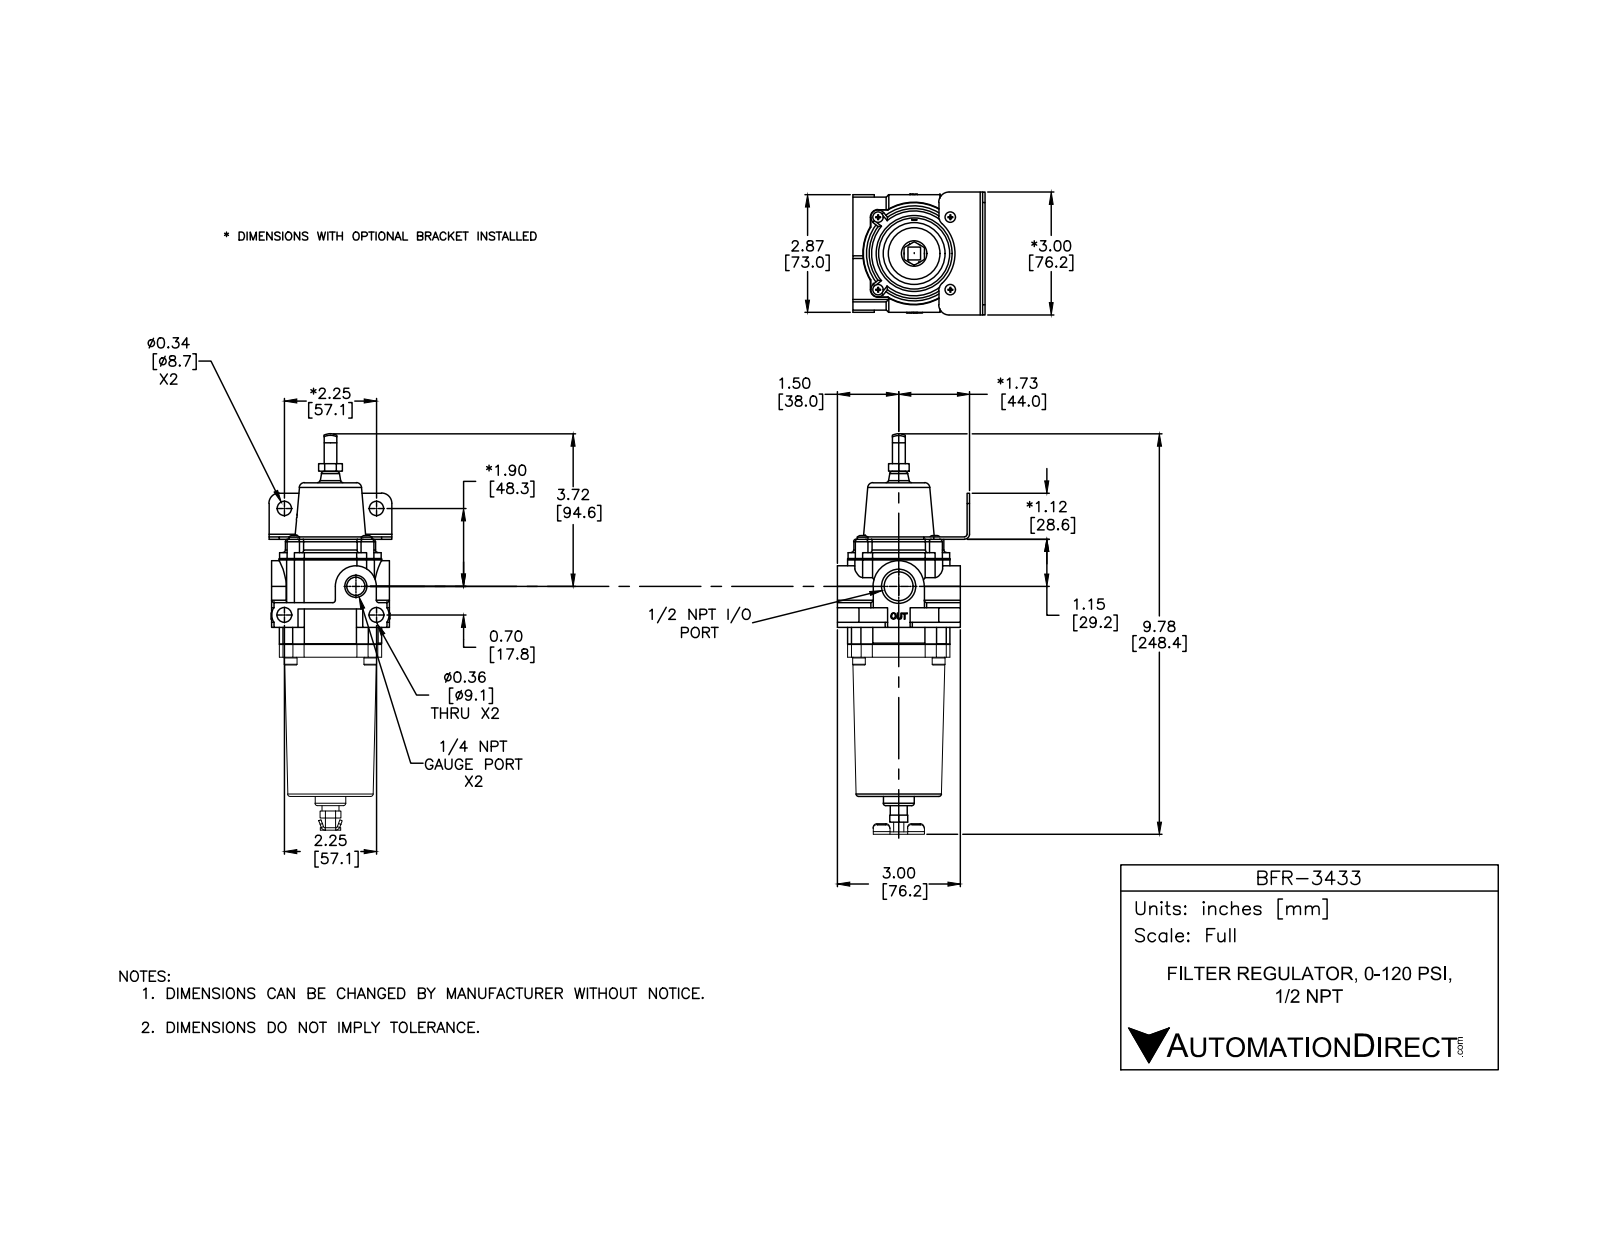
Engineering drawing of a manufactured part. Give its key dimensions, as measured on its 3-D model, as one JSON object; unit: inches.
{"part_name": "BFR-3433", "step_written_by": "SolidWorks 2015 (CONFIG_CONTROL_DESIGN)", "units": "inches", "bodies": {"solids": 15, "faces": 1577, "planar": 336, "cylindrical": 1000, "other": 241}, "overall_size": [9.766, 3, 2.895], "volume_in3": 21.24, "surface_area_in2": 150.8, "round_holes": [[0.159, 8], [0.201, 4], [0.207, 4], [0.36, 2], [0.125, 1], [0.257, 1], [0.26, 1], [0.438, 1], [0.703, 1]], "round_bosses_or_shafts": [[0.19, 8], [0.149, 8], [0.312, 5], [0.373, 4], [2.142, 1], [0.75, 1], [0.512, 1], [0.416, 1]], "partial_cylinders_radius": [[0.004, 48], [0.188, 12], [0.1, 8], [0.02, 6], [0.062, 5], [0.063, 5], [0.187, 4], [0.039, 2]], "face_to_face_distances": [2.075, 3.715, 5.79, 0.14, 3.575, 5.65, 4.13, 3.99, 0.415, 1.66], "hole_center_spacings": [1.858, 0.125, 1.944, 1.375, 1.25, 1.25, 1.768, 1.768]}
